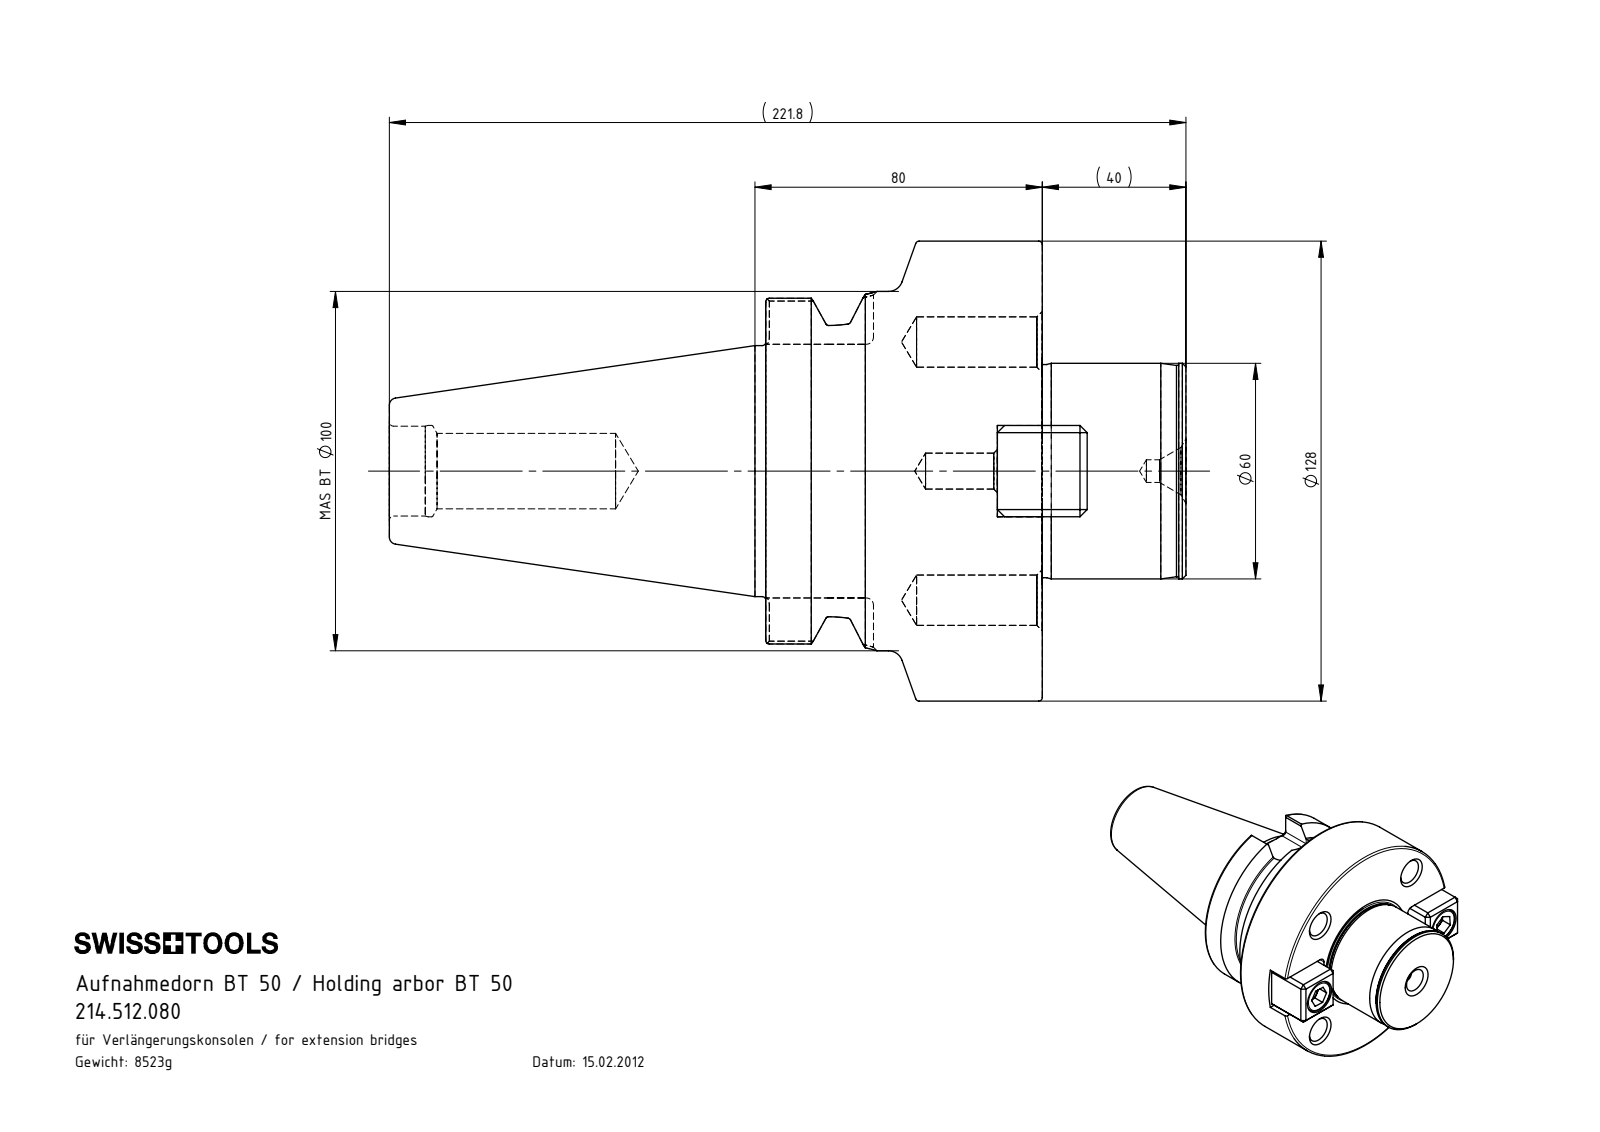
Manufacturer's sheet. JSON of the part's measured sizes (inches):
{"part_name": "U00-D60.ER1.025; ISO 4762 - M12 x 25_PreviewCfg; BT5-D60.K01.080", "step_written_by": "SolidWorks 2017 (CONFIG_CONTROL_DESIGN)", "units": "inches", "bodies": {"solids": 5, "faces": 274, "planar": 99, "cylindrical": 68, "other": 107}, "overall_size": [8.732, 5.039, 5.039], "volume_in3": 66.27, "surface_area_in2": 160.6, "round_holes": [[0.551, 4], [0.394, 2], [0.512, 2], [0.748, 2], [0.248, 1], [0.827, 1], [0.984, 1], [1.002, 1]], "round_bosses_or_shafts": [[0.709, 2], [0.472, 2], [5.039, 1], [3.937, 1], [3.346, 1], [2.75, 1], [2.362, 1], [2.335, 1]], "partial_cylinders_radius": [[0.079, 8], [0.118, 4], [0.506, 1]], "face_to_face_distances": [3.031, 1, 0.492, 4.606, 1.575, 2.539, 2.067, 0.89, 1.89, 3.858], "hole_center_spacings": [1.505, 2, 2.828, 3.63, 1.929, 4, 3.858]}
